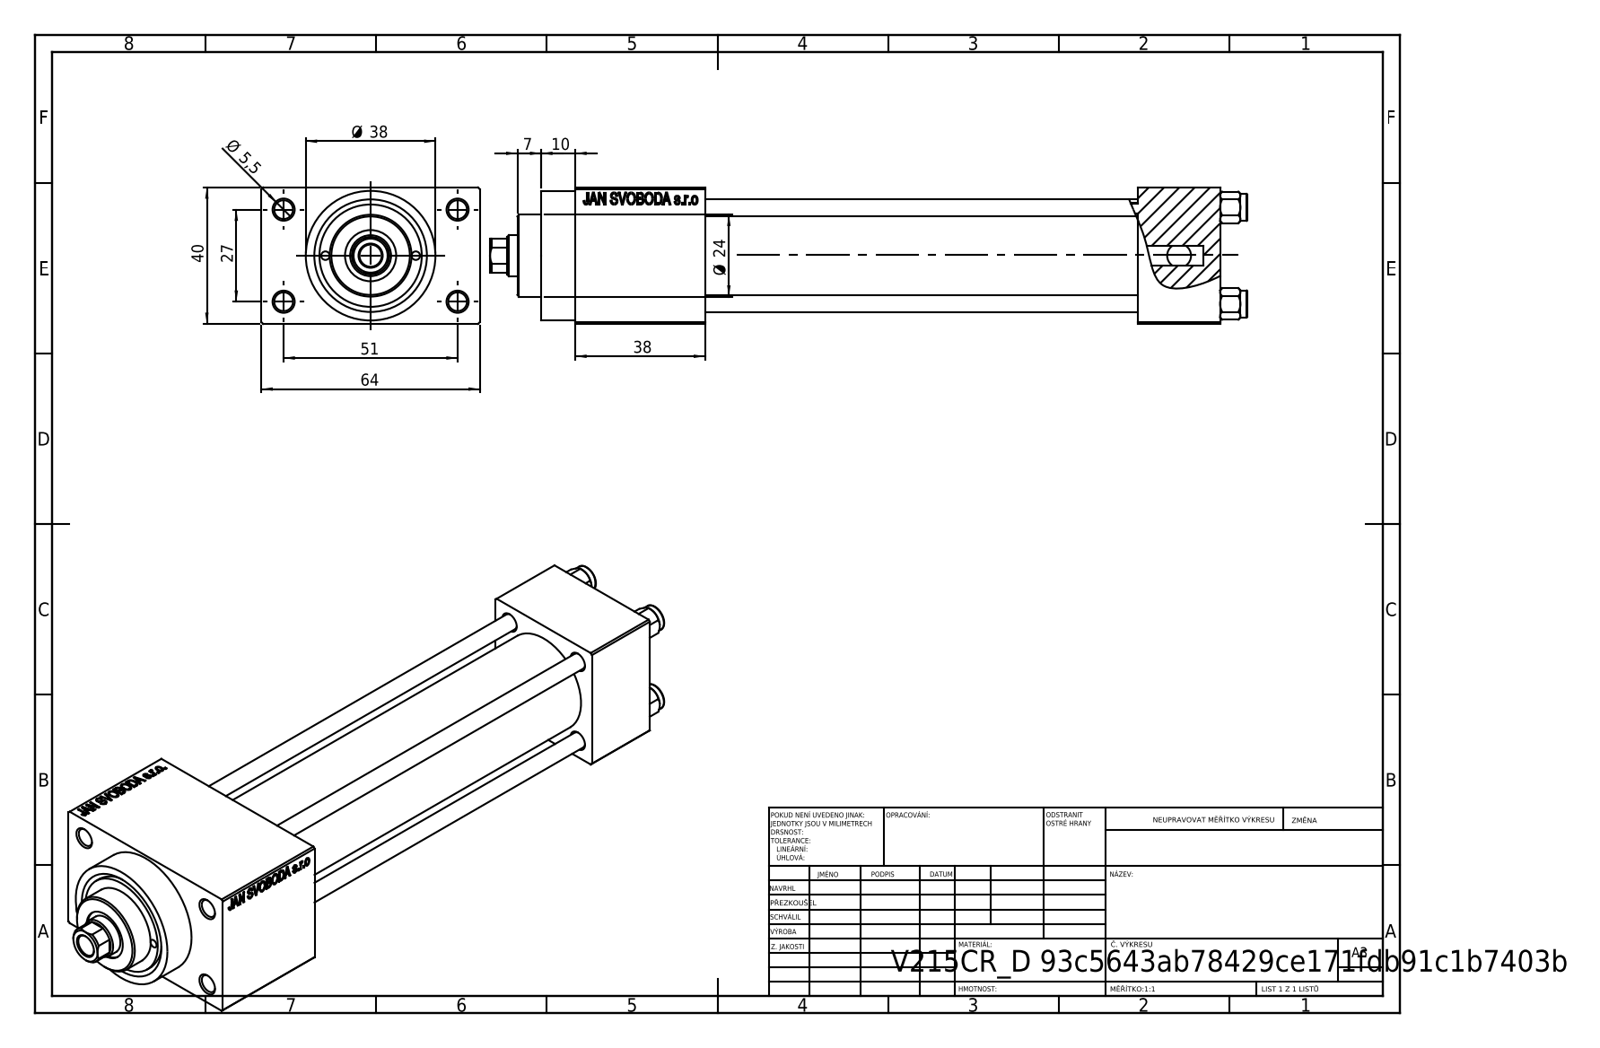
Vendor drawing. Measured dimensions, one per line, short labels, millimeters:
name: V215CR_D_TYCINKA; V215CR_D_Body; V215_VC_A; NUT_M5_D (+1 more)
written by: SolidWorks 2019 (CONFIG_CONTROL_DESIGN)
unit: mm
bodies: 11 solids, 1110 faces (498 planar, 92 cylindrical, 520 other)
size: 222 × 64 × 40
volume: 209 967 mm³; area: 84 275 mm²
holes: 4× ⌀5, 4× ⌀5.5, 3× ⌀20, 2× ⌀2.5, 2× ⌀7, 2× ⌀13.16, 1× ⌀6.5, 1× ⌀12, 1× ⌀15, 1× ⌀25, 1× ⌀30
bosses: 4× ⌀8, 1× ⌀38, 1× ⌀31, 1× ⌀24
rounds: 1× R5.5
face distances: 40, 12, 127, 24, 151, 52, 38, 189, 165, 64
hole spacings: 11.37, 14.18, 18.23, 20.01, 28.3, 28.85, 29.89, 30.84
